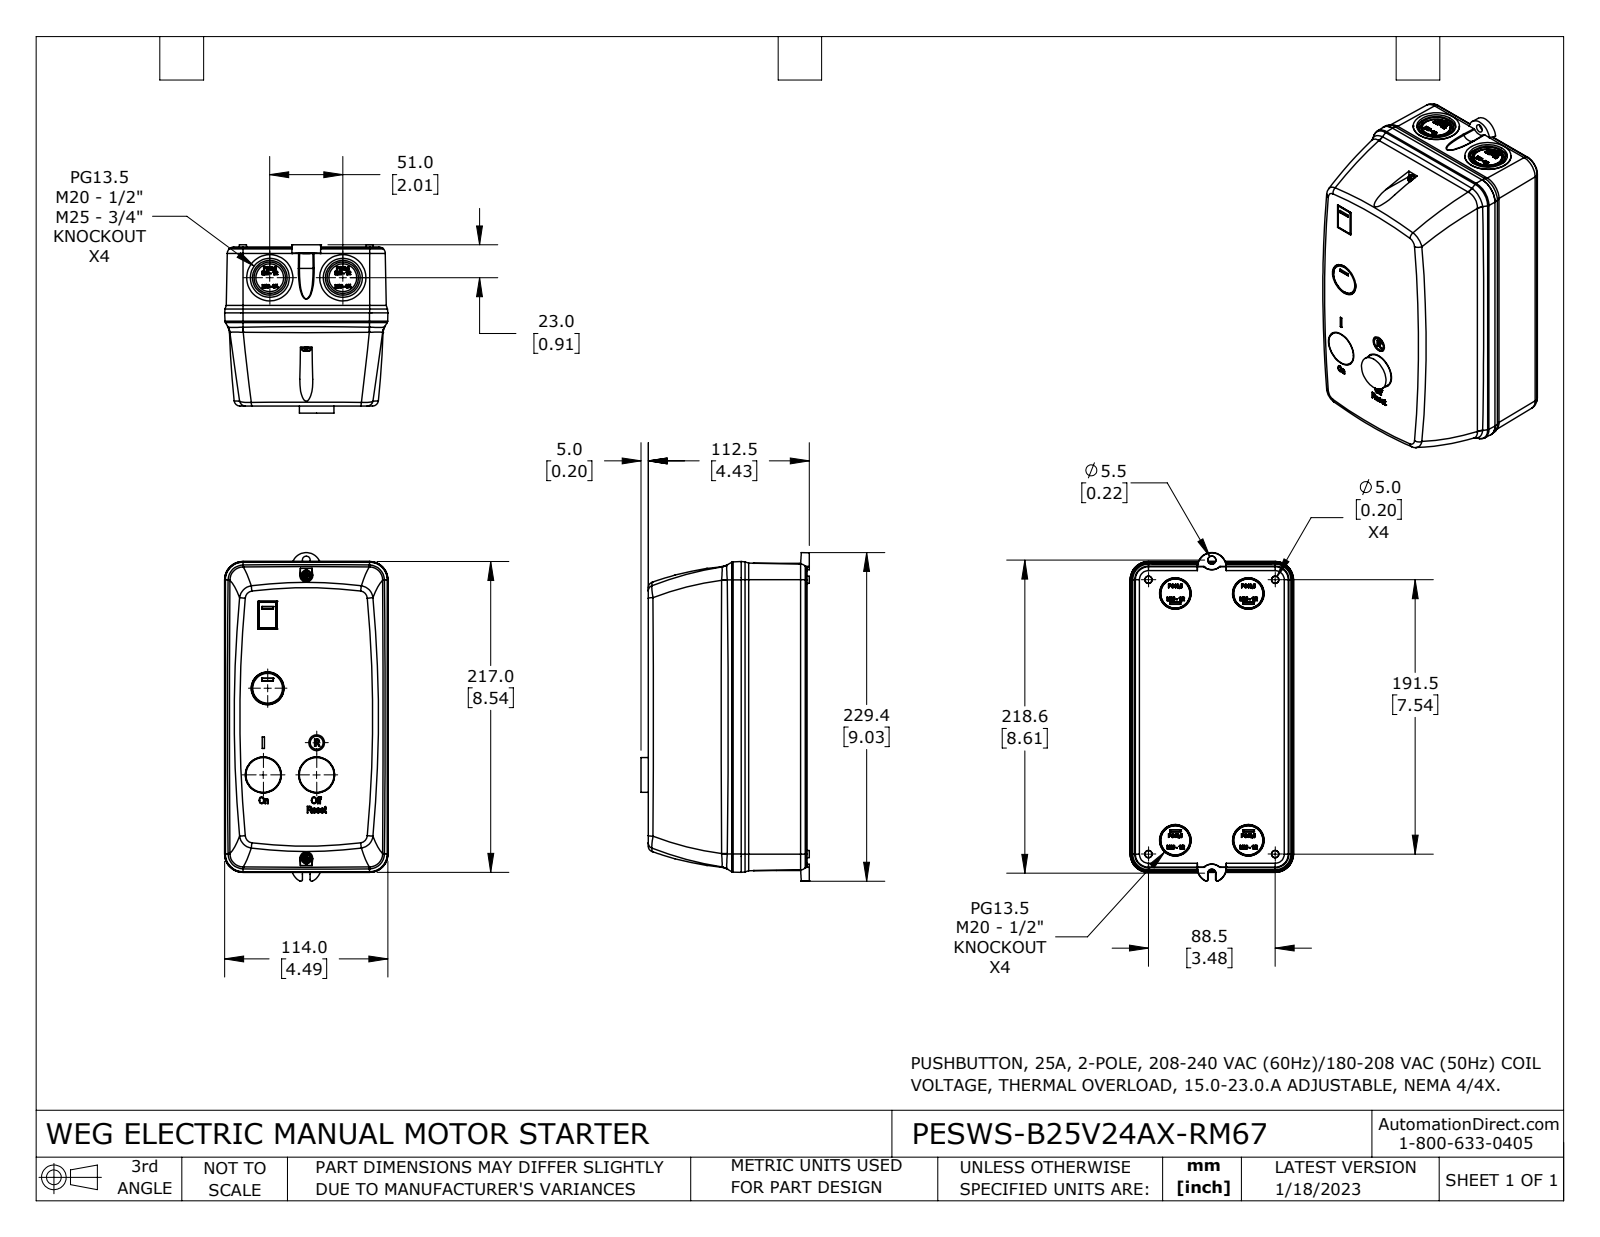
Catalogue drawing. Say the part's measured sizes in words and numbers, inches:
The part is named "PESWS-B25V24AX-RM67". Its 3-D file was written by "SolidWorks 2021 (CONFIG_CONTROL_DESIGN)". It is 6 solids with 2195 faces: 1110 planar, 92 cylindrical and 993 other. Overall it measures 9.033 by 4.626 by 4.489 inches. Its volume is 149.9 cubic inches and its surface area 257.6 square inches. Round holes: 2 of diameter 0.173, 2 of diameter 0.863, 2 of diameter 1.072, 1 of diameter 0.217, 1 of diameter 0.433. Round bosses or shafts: 2 of diameter 1.27, 2 of diameter 0.955, 2 of diameter 0.953, 2 of diameter 0.763, 2 of diameter 0.276, 2 of diameter 0.118, 1 of diameter 0.354. Partial cylindrical surfaces (rounded edges, fillets, slot ends): 4 of radius 0.079, 4 of radius 0.181, 4 of radius 0.376, 2 of radius 0.257, 2 of radius 0.297, 1 of radius 0.082, 1 of radius 0.085, 1 of radius 0.108. The main face-to-face distances are 1.811, 2.559, 4.37, 0.02, 4.35, 1.791, 4.331, 0.039, 4.311, 2.52. The hole center spacings are 0.413, 2.008, 3.202, 4.615, 5.028, 7.795, 8.209.
